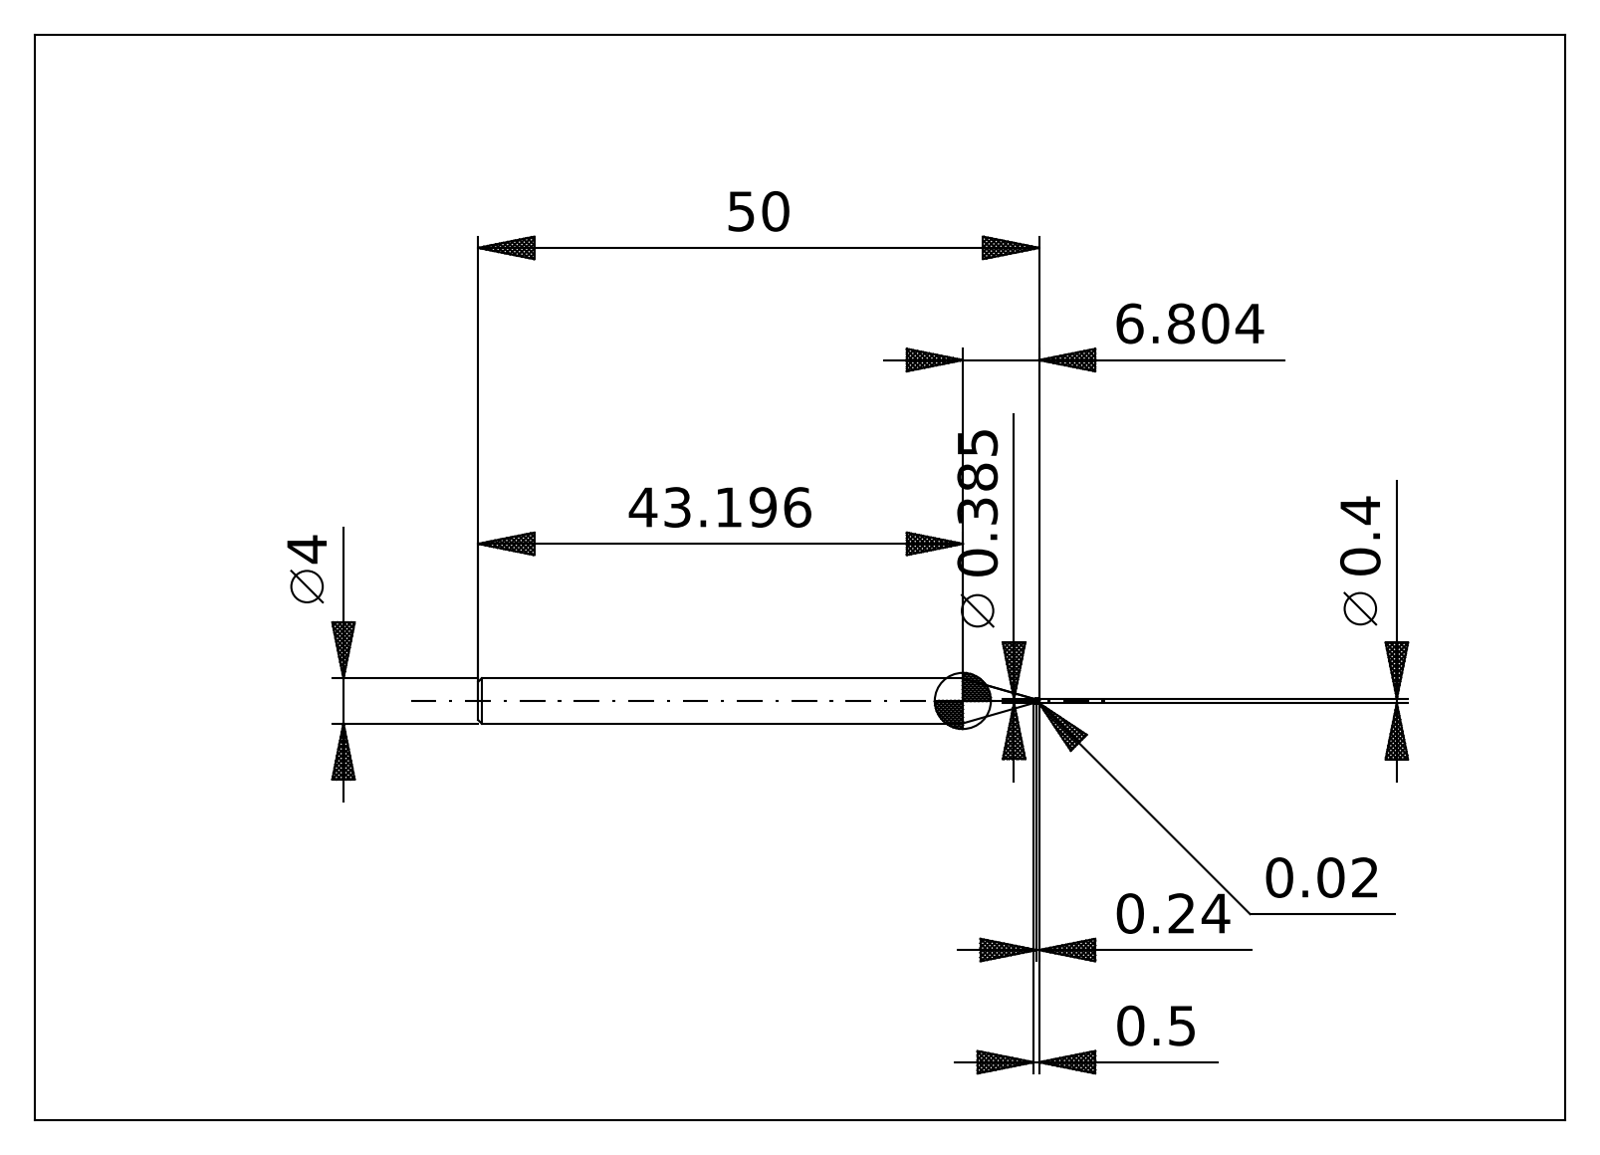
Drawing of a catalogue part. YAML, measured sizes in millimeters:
step_written_by: "ACIS (automotive_design)"
units: millimeters
bodies: {solids: 2, faces: 26, planar: 6, cylindrical: 8, other: 12}
overall_size: [50, 4, 4]
volume: 572
surface_area: 599
round_bosses_or_shafts:
  - {diameter: 4, count: 1}
  - {diameter: 0.38, count: 1}
face_to_face_distances: [50, 49.94, 49.76, 6.8, 6.74, 6.56, 43.2]
